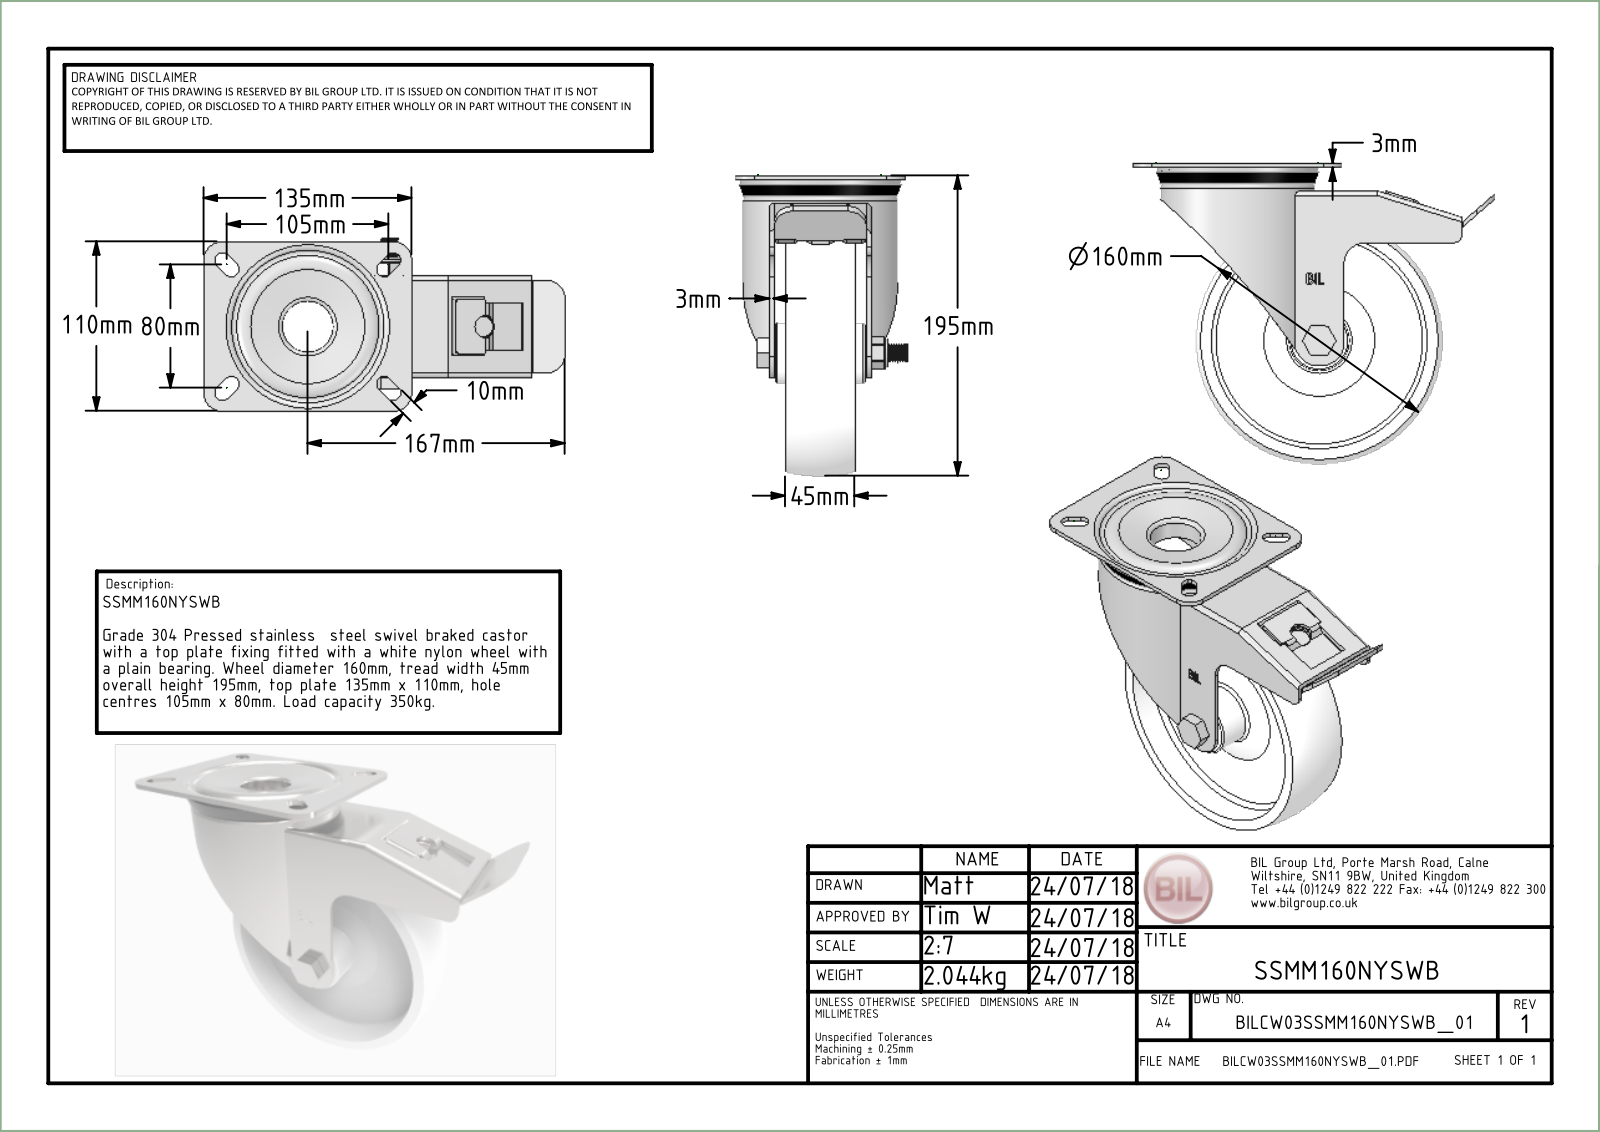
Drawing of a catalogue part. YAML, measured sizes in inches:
part_name: "SSMM160NYSWB v4; SSMM150ASSWB v1; ZINC PLATED, PRESSED STEEL TOP PLATE; ZINC PLATED, PRESSED STEEL TOP PLATE Geometry (+7 more)"
step_written_by: "Autodesk Translation Framework v14.10.0.0 (AUTOMOTIVE_DESIGN)"
units: inches
bodies: {solids: 56, faces: 591, planar: 246, cylindrical: 172, other: 173}
overall_size: [9.232, 7.677, 4.431]
volume: 34.78
surface_area: 367.9
round_holes:
  - {diameter: 0.315, count: 1}
  - {diameter: 0.433, count: 1}
  - {diameter: 0.472, count: 1}
  - {diameter: 0.48, count: 1}
  - {diameter: 0.492, count: 1}
  - {diameter: 0.551, count: 1}
  - {diameter: 0.807, count: 1}
  - {diameter: 1.329, count: 1}
  - {diameter: 1.565, count: 1}
  - {diameter: 3.622, count: 1}
  - {diameter: 5.512, count: 1}
round_bosses_or_shafts:
  - {diameter: 3.819, count: 1}
  - {diameter: 3.071, count: 1}
  - {diameter: 1.969, count: 1}
  - {diameter: 1.535, count: 1}
  - {diameter: 0.783, count: 1}
  - {diameter: 0.728, count: 1}
  - {diameter: 0.699, count: 1}
  - {diameter: 0.551, count: 1}
partial_cylinders:
  - {radius: 0.01, count: 18}
  - {radius: 0.02, count: 18}
  - {radius: 0.059, count: 10}
  - {radius: 0.217, count: 10}
  - {radius: 0.118, count: 8}
  - {radius: 0.098, count: 6}
  - {radius: 0.394, count: 4}
  - {radius: 0.039, count: 3}
face_to_face_distances: [0.276, 0.118, 0.098, 0.354, 1.142, 1.417, 1.043, 2.461, 1.319, 0.197]
hole_center_spacings: [2.638]
